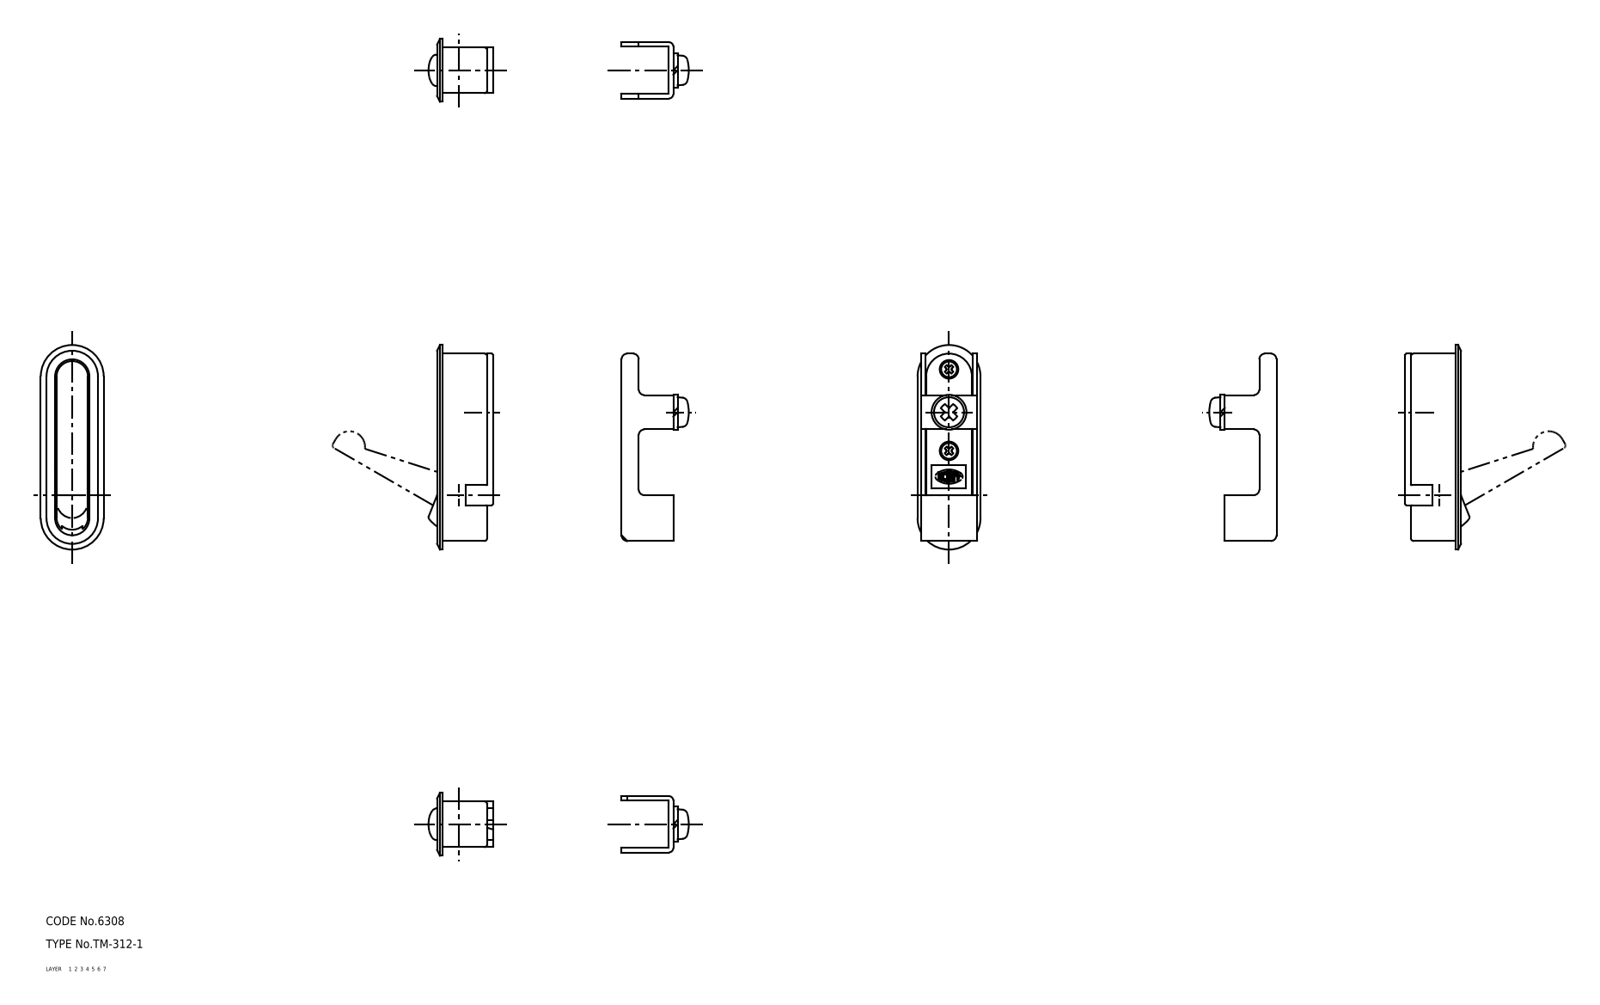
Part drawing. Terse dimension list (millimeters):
name: 67122663; 67122676; 67122689
written by: CADfix (AUTOMOTIVE_DESIGN)
unit: mm
bodies: 3 solids, 297 faces (0 planar, 0 cylindrical, 297 other)
size: 71.5 × 29.42 × 22
volume: 18 741 mm³; area: 15 946 mm²
